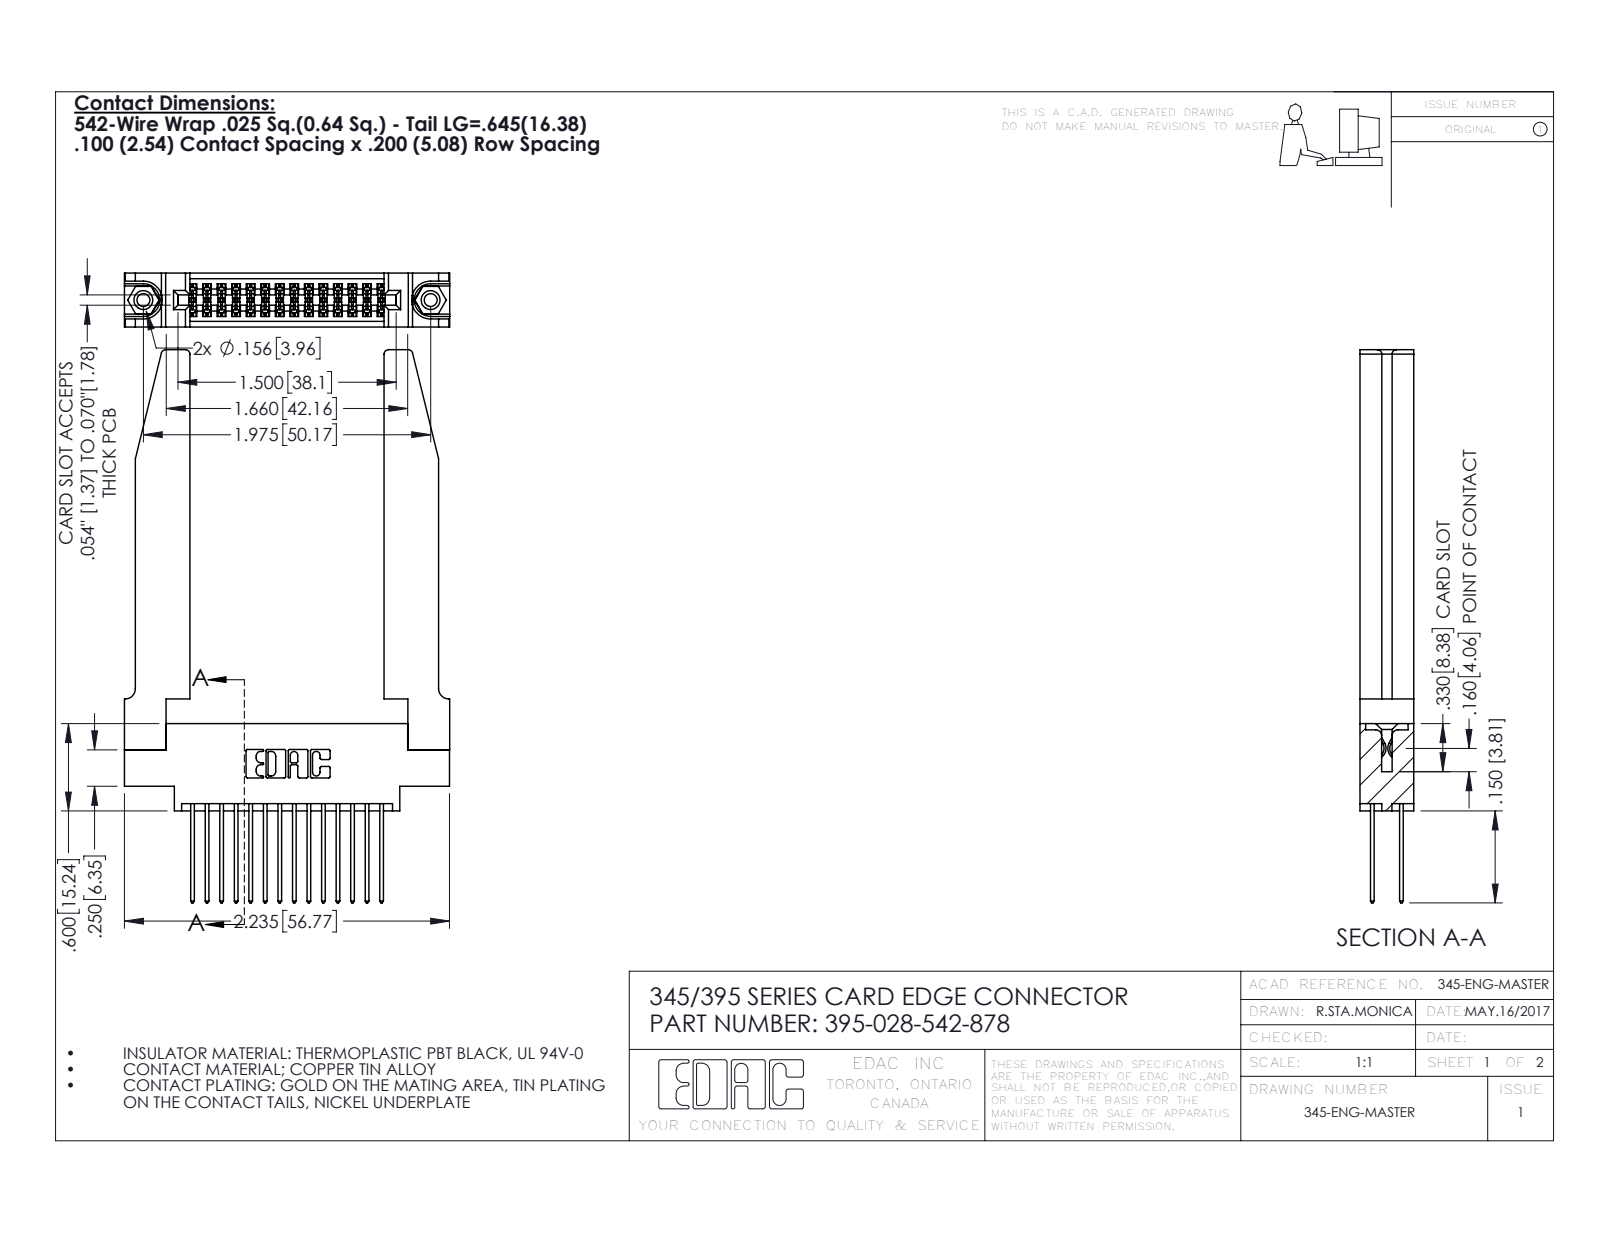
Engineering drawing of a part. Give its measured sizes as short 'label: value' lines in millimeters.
name: 345-292-001_345-293-142; 395-028-542-878; 345 Part_0.170 Offset - 0.156 Dia-TH; 345-250-001_345-250-001-102 (+1 more)
written by: SolidWorks 2016 (CONFIG_CONTROL_DESIGN)
unit: mm
bodies: 33 solids, 1764 faces (1150 planar, 562 cylindrical, 52 other)
size: 96.6 × 56.8 × 9.4
volume: 13 000 mm³; area: 14 850 mm²
holes: 2× ⌀2.3, 2× ⌀3.2, 2× ⌀4, 1× ⌀1.6
bosses: 2× ⌀3.9
rounds: 42× R0.2, 28× R0.3, 22× R0.3, 8× R0.8, 6× R0.2, 6× R0.8, 3× R0.7, 2× R0.4
face distances: 9.4, 1.8, 7.6, 5.1, 2.5, 6.9, 0.6, 3.8, 3.8, 5.7
hole spacings: 6.9, 44.2, 50.2
